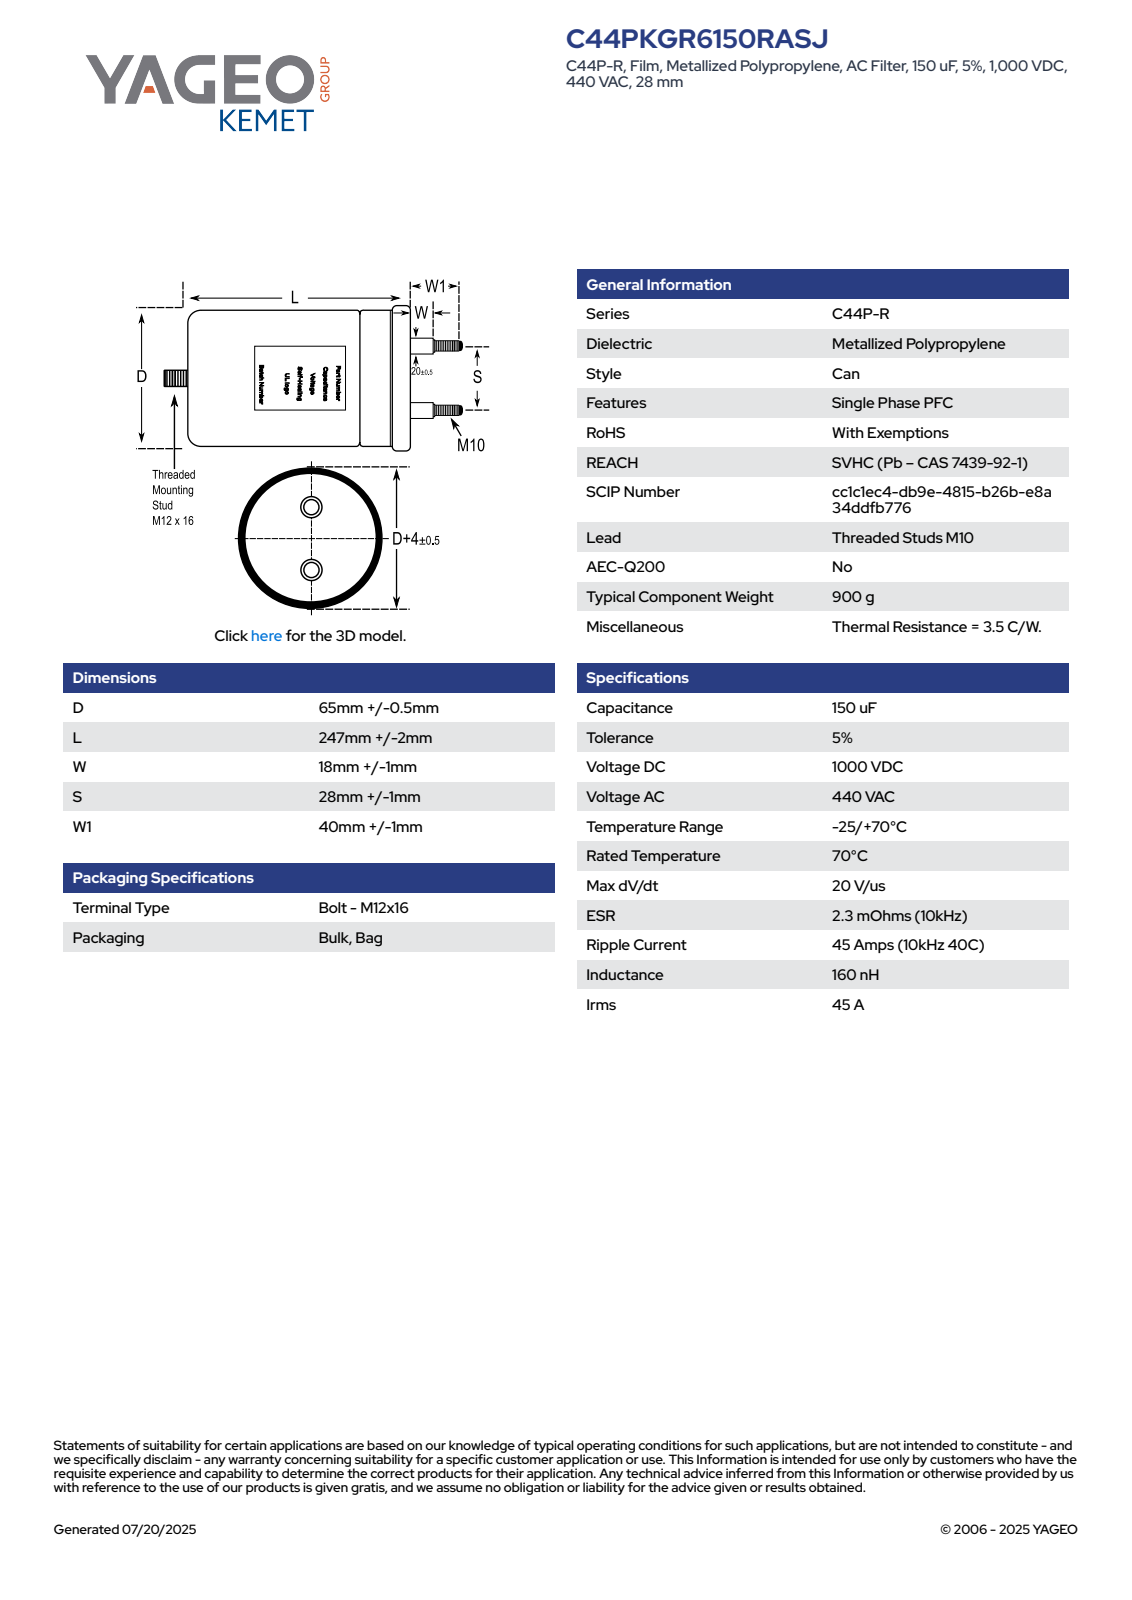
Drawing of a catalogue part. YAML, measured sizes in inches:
part_name: "CFP_C44P_65X247_D65.5L249S28"
step_written_by: "SolidWorks 2014 (AUTOMOTIVE_DESIGN)"
units: inches
bodies: {solids: 1, faces: 105, planar: 32, cylindrical: 36, other: 37}
overall_size: [12.047, 2.756, 2.756]
volume: 52.42
surface_area: 97.32
round_bosses_or_shafts:
  - {diameter: 0.472, count: 3}
  - {diameter: 0.807, count: 2}
  - {diameter: 0.394, count: 2}
  - {diameter: 2.756, count: 1}
  - {diameter: 2.579, count: 1}
partial_cylinders:
  - {radius: 1.29, count: 1}
face_to_face_distances: [9.803, 10.512, 0.709, 9.489, 0.315, 1.023, 11.417, 1.929, 1.614, 0.906]
